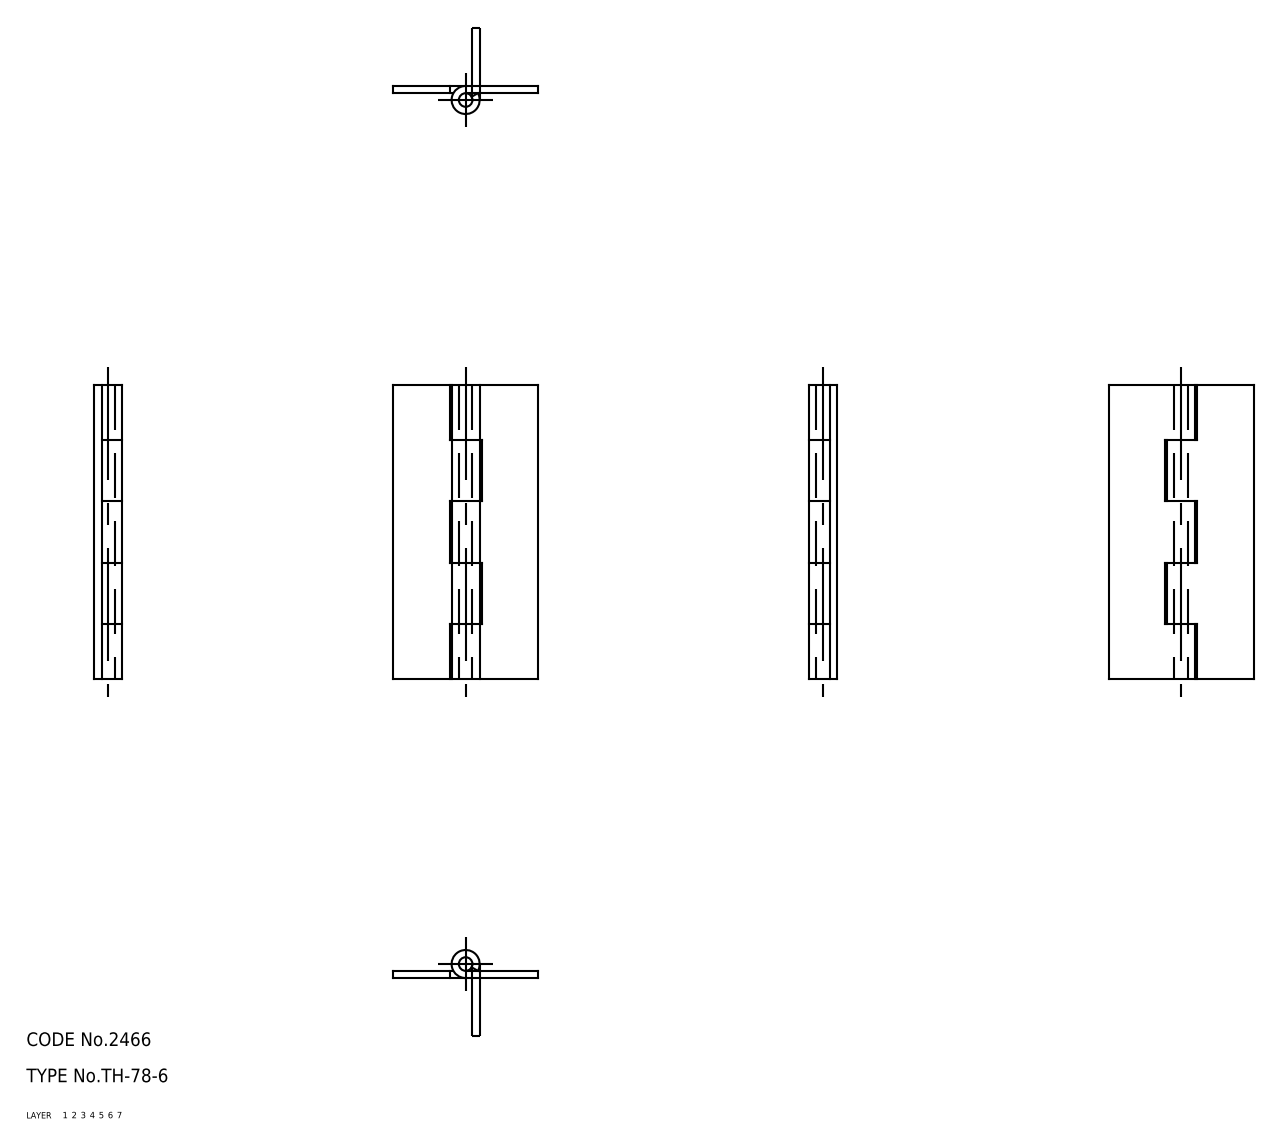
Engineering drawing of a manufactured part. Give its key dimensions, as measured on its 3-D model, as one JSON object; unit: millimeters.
{"part_name": "hinge piece_B; hinge piece_A; shaft; TH_78_6_16821_36", "step_written_by": "CADfix (AUTOMOTIVE_DESIGN)", "units": "millimeters", "bodies": {"solids": 3, "faces": 42, "planar": 0, "cylindrical": 0, "other": 42}, "overall_size": [65, 32, 6.2], "volume_mm3": 4668, "surface_area_mm2": 6631}
